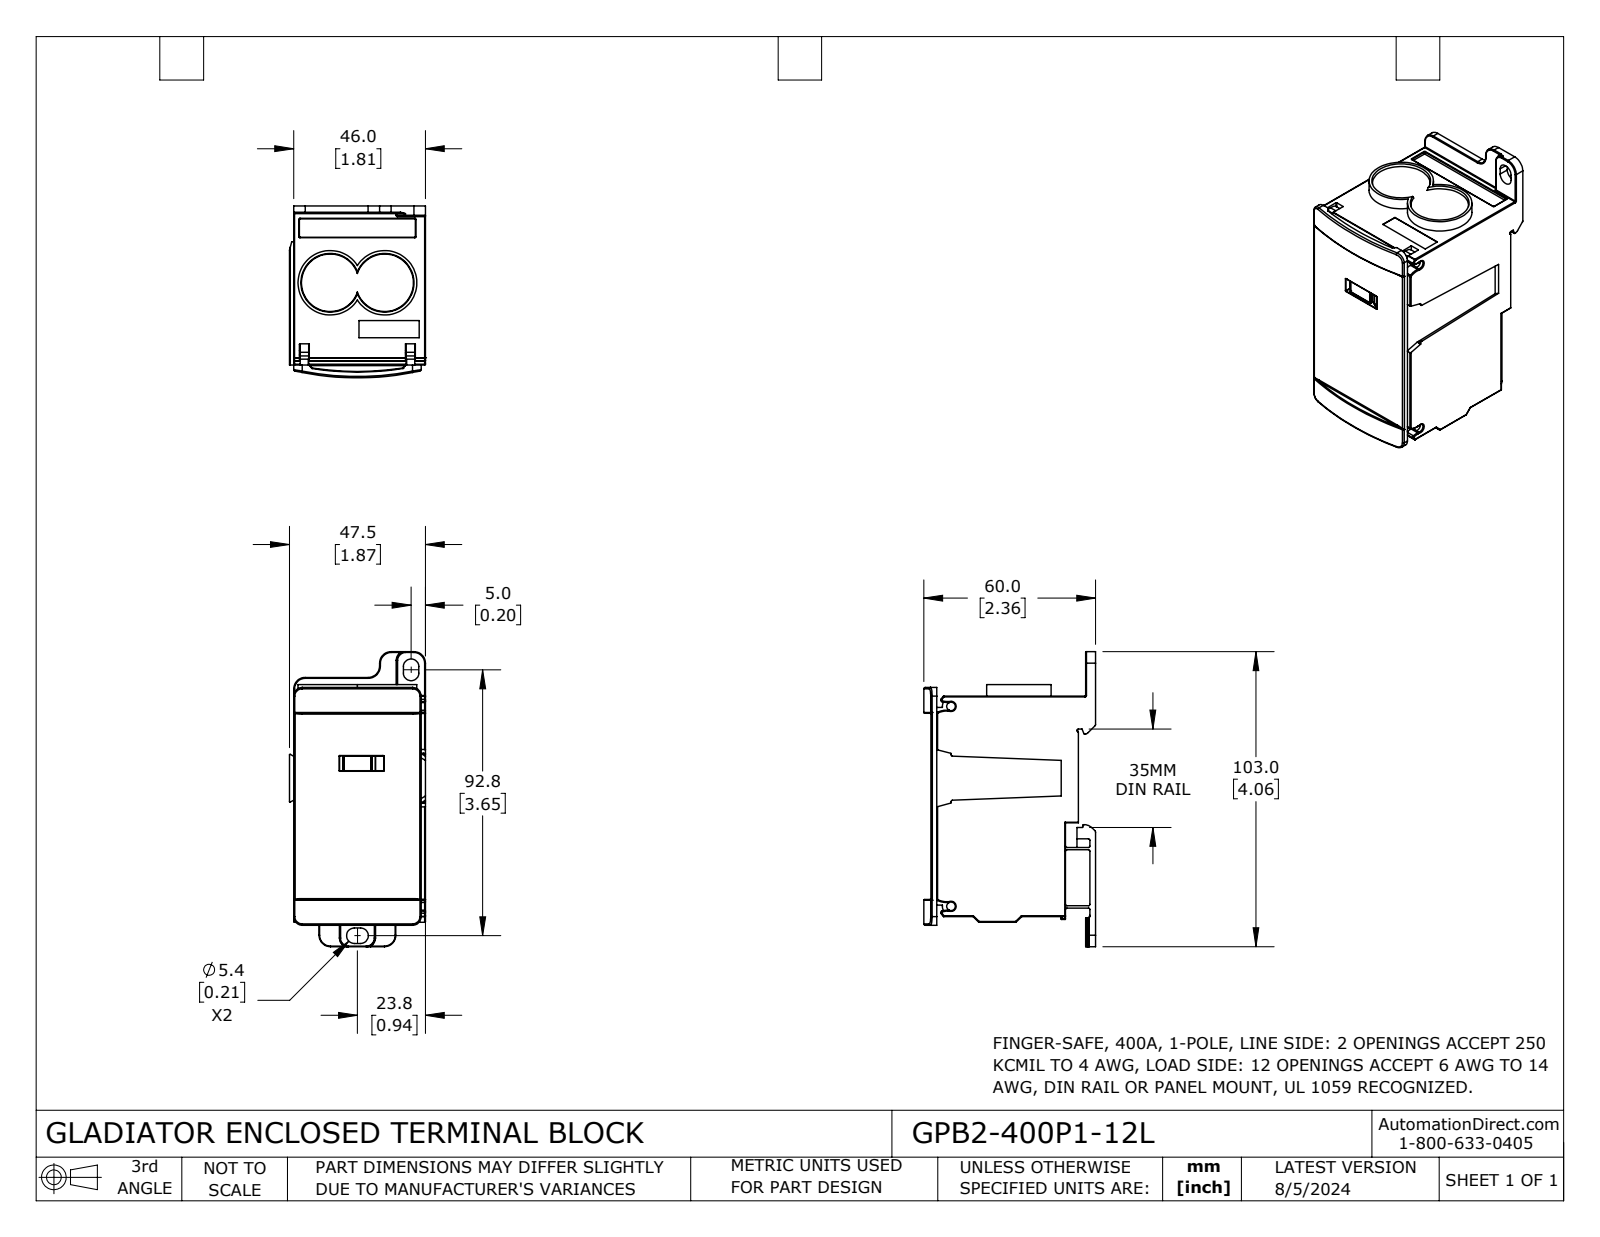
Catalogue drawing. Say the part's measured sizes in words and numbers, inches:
The part is named "GPB2-400P1-12L". Its 3-D file was written by "SolidWorks 2023 (CONFIG_CONTROL_DESIGN)". It is 1 solid with 645 faces: 218 planar, 287 cylindrical and 140 other. Overall it measures 4.055 by 2.362 by 1.87 inches. Its volume is 11.41 cubic inches and its surface area 43.2 square inches. Round holes: 6 of diameter 0.394, 2 of diameter 0.118. Round bosses or shafts: 2 of diameter 0.886. Partial cylindrical surfaces (rounded edges, fillets, slot ends): 60 of radius 0.008, 34 of radius 0.012, 25 of radius 0.004, 23 of radius 0.02, 9 of radius 0.118, 7 of radius 0.157, 6 of radius 0.197, 4 of radius 0.106. The main face-to-face distances are 1.811, 0.039, 2.264, 0.236, 2.028, 0.118, 2.992, 0.079, 3.031, 0.177. The hole center spacings are 0.433, 1.236, 1.157, 0.866, 1.446, 2.748.
